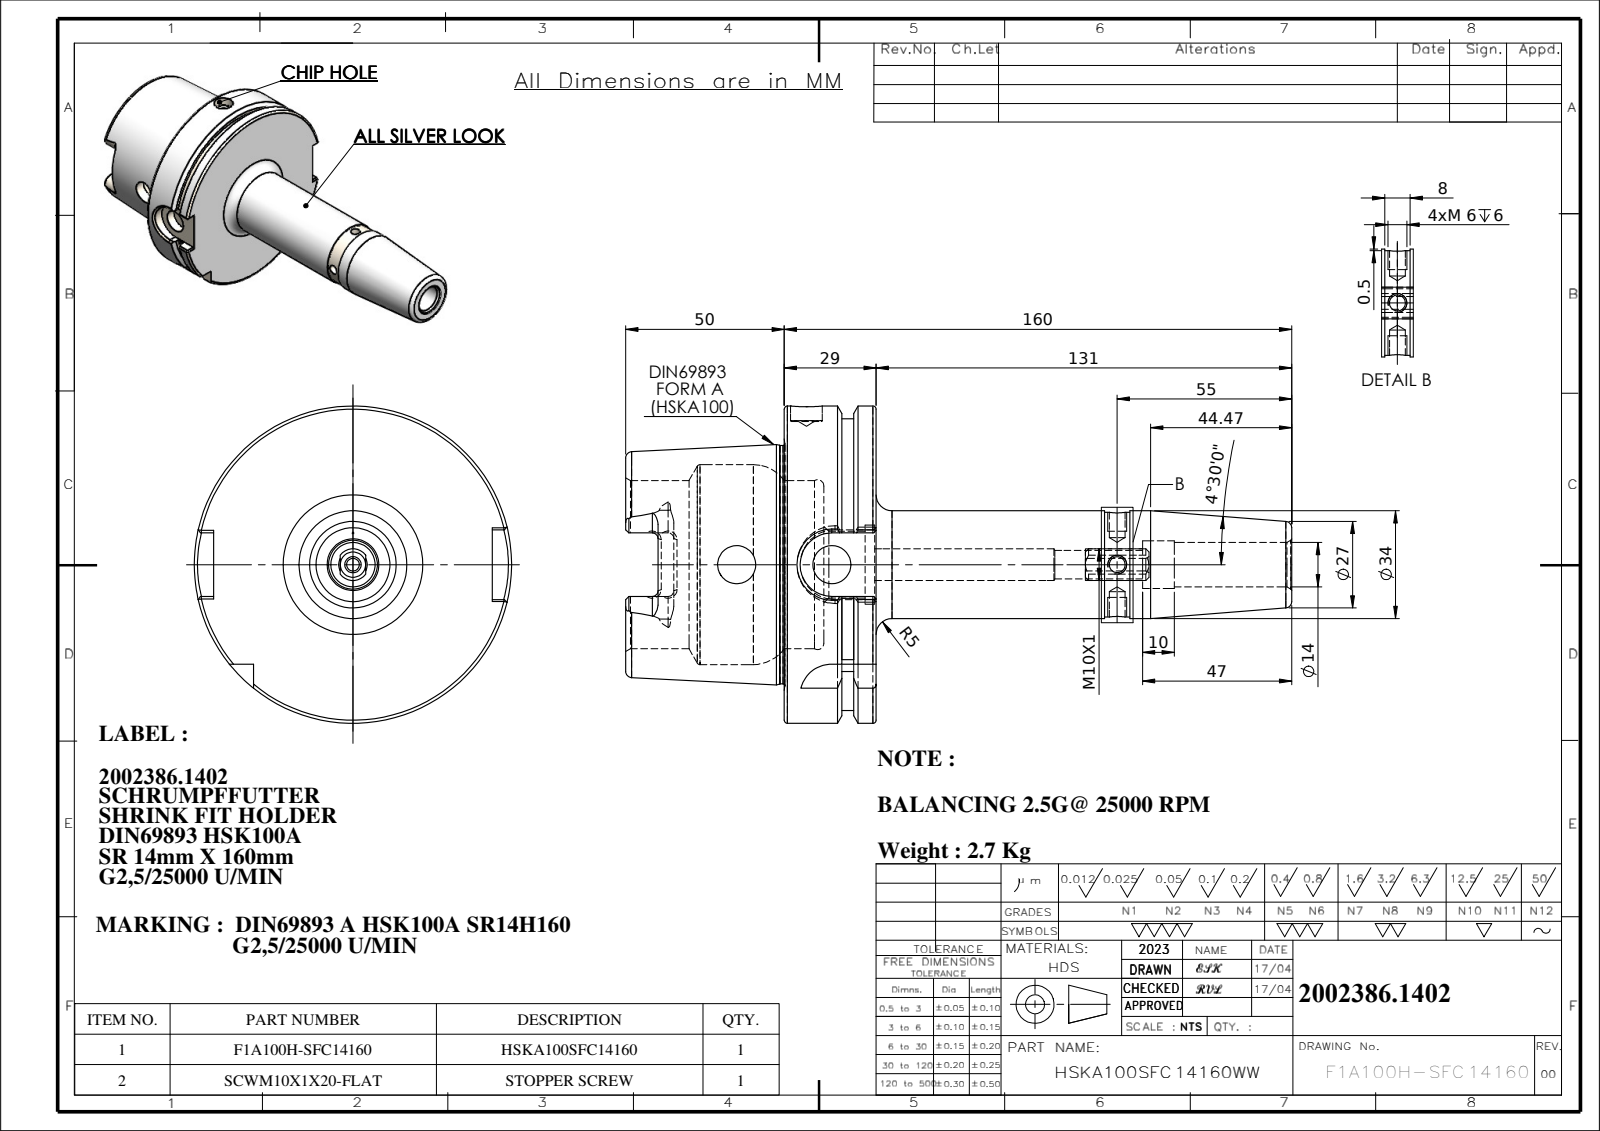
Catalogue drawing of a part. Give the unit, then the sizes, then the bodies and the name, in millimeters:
Units: millimetres
Overall size (bounding box): 209.95 × 100 × 100
Round holes (diameter × count): ⌀5 ×2, ⌀12 ×2, ⌀4 ×1, ⌀9 ×1, ⌀10 ×1, ⌀13.99 ×1, ⌀14.99 ×1, ⌀21 ×1, ⌀25 ×1, ⌀53 ×1, ⌀63 ×1
Round bosses / shafts (diameter × count): ⌀100 ×1, ⌀92 ×1, ⌀75.16 ×1, ⌀34 ×1, ⌀33 ×1, ⌀10 ×1
Partial cylindrical surfaces — rounded edges, fillets, slot ends (radius × count): R1.8 ×6, R4.88 ×4, R10 ×2, R11 ×1
Main face-to-face distances: 28.95, 12.5, 16.45, 50, 62.5, 78.95, 78.5, 28.5, 16, 0.45
Hole centre spacings: 30, 89.95, 97.95, 119.95
Volume: 351 758 mm³ · Surface area: 68 876 mm²
Bodies: 2 solids, 220 faces (59 planar, 71 cylindrical, 90 other)
Part name (STEP PRODUCT): HSKA100SFC14160WW; SCWM10X1X20-FLAT; 91100A-SR14160
STEP written by: SolidWorks 2018 (CONFIG_CONTROL_DESIGN)
